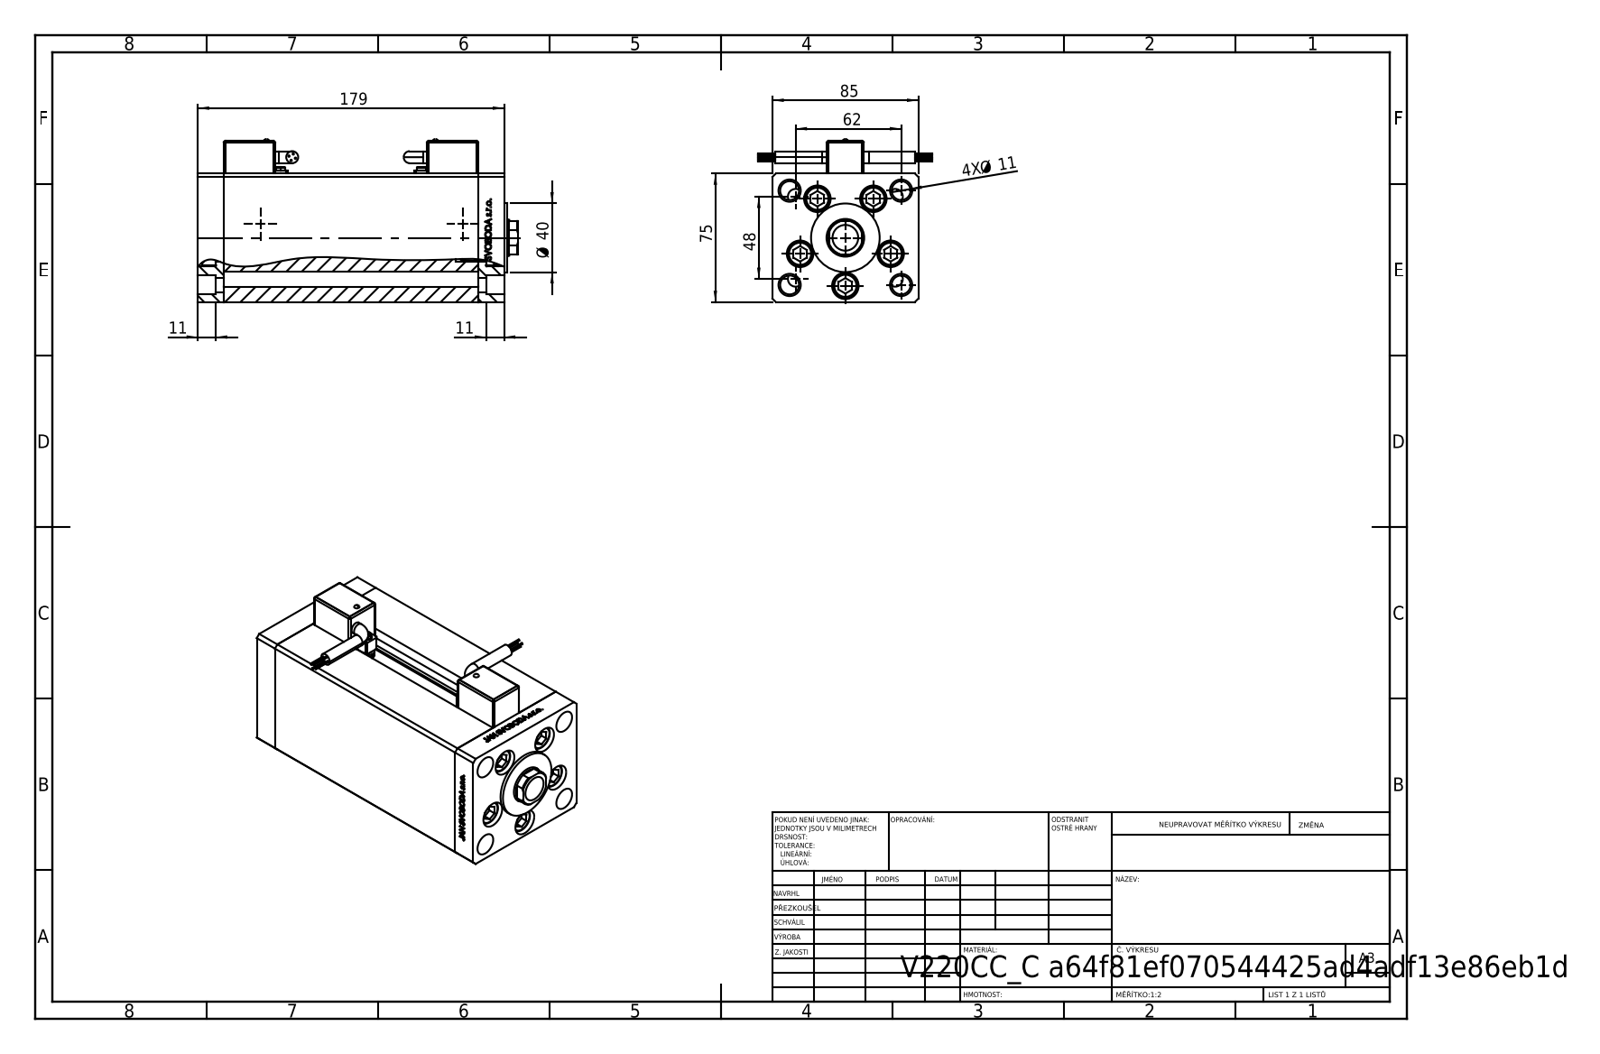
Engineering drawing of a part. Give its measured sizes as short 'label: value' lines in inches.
name: V220C_C MIDDLE; V220C_C CAST PRO VYSUNUTI; ALLEN BOLT; Magnetic_Switch_MSU4 (+2 more)
written by: SolidWorks 2019 (CONFIG_CONTROL_DESIGN)
unit: in
bodies: 16 solids, 1377 faces (624 planar, 249 cylindrical, 504 other)
size: 7.343 × 4 × 3.744
volume: 61.33 in³; area: 288.2 in²
holes: 9× ⌀0.433, 5× ⌀0.61, 4× ⌀0.354, 4× ⌀0.512, 2× ⌀0.142, 2× ⌀0.197, 2× ⌀0.276, 1× ⌀0.591, 1× ⌀0.866
bosses: 8× ⌀0.033, 5× ⌀0.571, 5× ⌀0.315, 4× ⌀0.276, 2× ⌀0.236, 2× ⌀0.138, 2× ⌀0.098, 1× ⌀1.575
rounds: 24× R0.039, 4× R0.157, 2× R0.037, 1× R0.413
face distances: 3.346, 2.953, 5.846, 0.591, 6.437, 0.413, 7.028, 2.697, 0.256, 1.248
hole spacings: 1.102, 0.195, 1.482, 1.676, 2.032, 2.425, 3.158, 0.325
